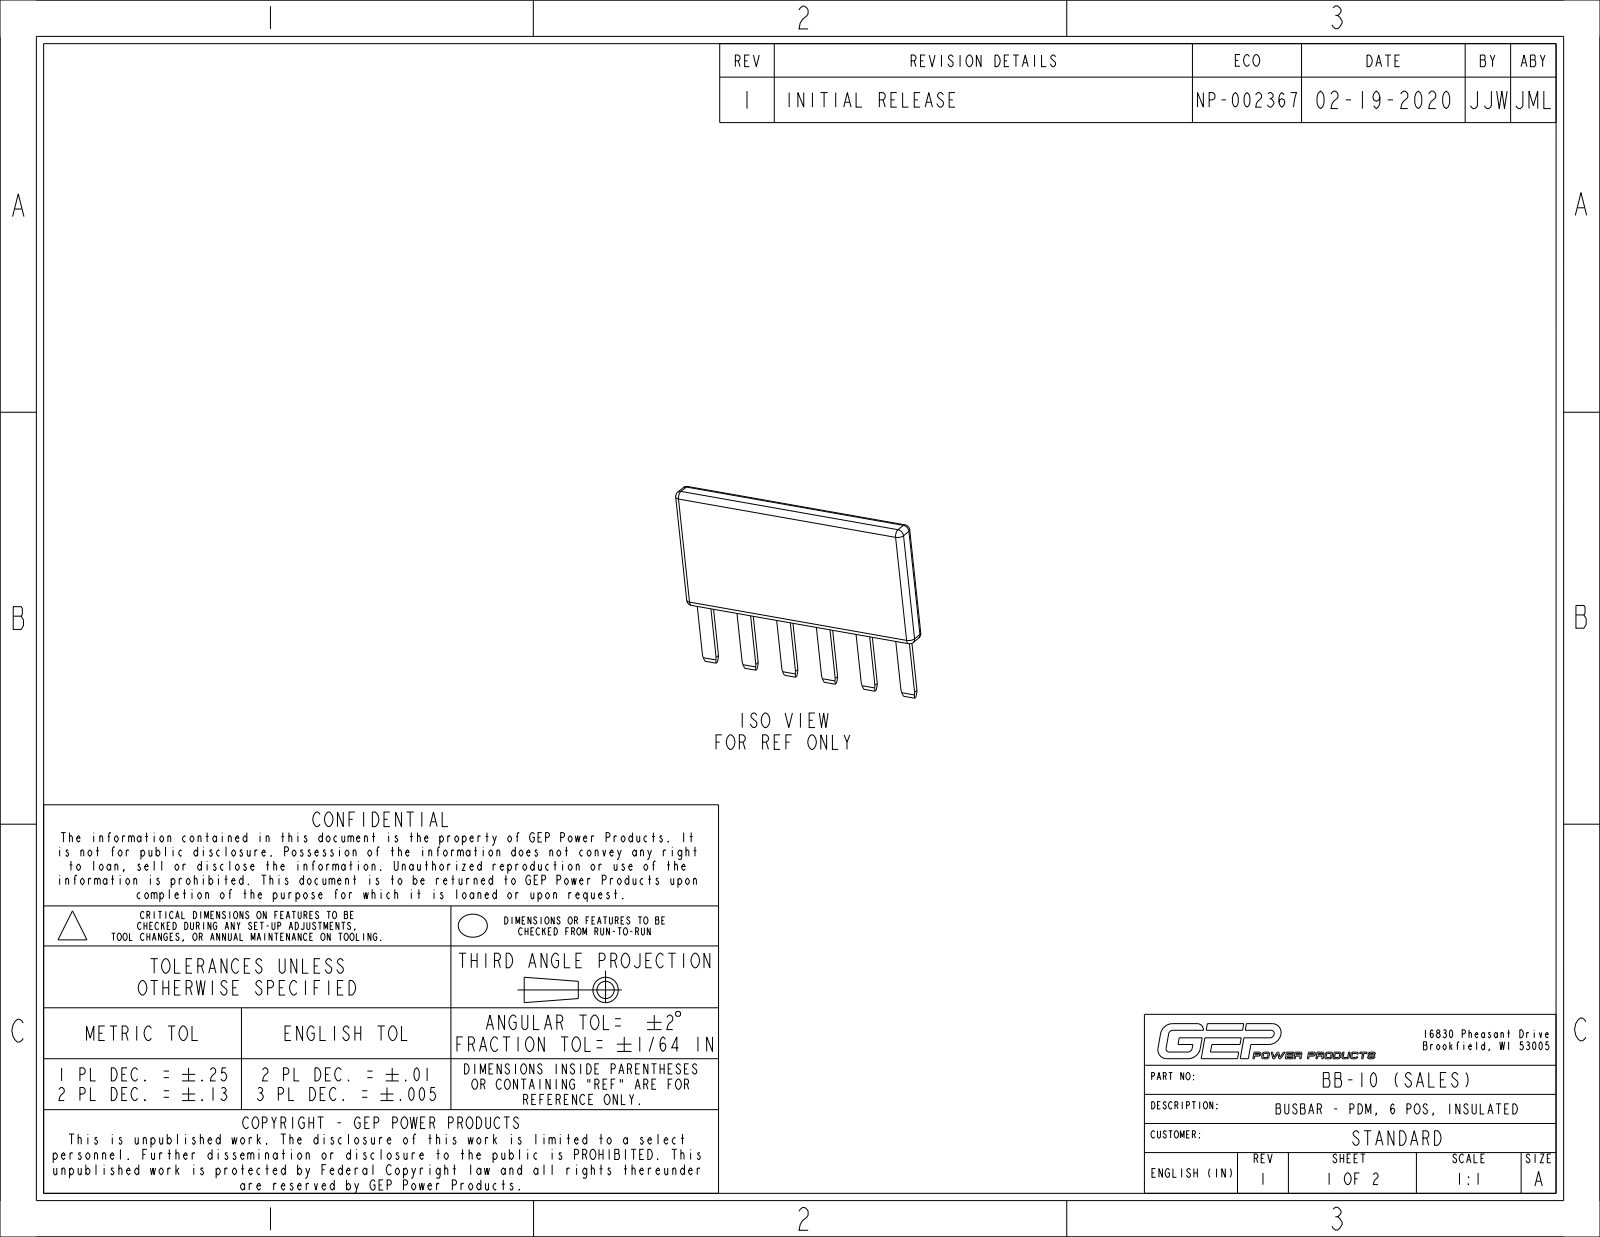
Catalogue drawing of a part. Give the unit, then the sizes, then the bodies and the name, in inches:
Units: inches
Overall size (bounding box): 1.83 × 1.31 × 0.152
Partial cylindrical surfaces — rounded edges, fillets, slot ends (radius × count): R0.04 ×12
Main face-to-face distances: 0.032, 0.06, 0.06, 0.092, 0.152, 0.092, 0.81, 0.75, 0.32, 0.87
Volume: 0.247 in³ · Surface area: 10.14 in²
Bodies: 2 solids, 96 faces (76 planar, 12 cylindrical, 8 other)
Part name (STEP PRODUCT): Q-BB-10_BAR_NCF; Q-BB-10_MOLD_NCF; Q-BB-10_NCF_ASM; Q-BB-10_SALES_NCF_ASM
STEP written by: CREO PARAMETRIC BY PTC INC, 2017110 (CONFIG_CONTROL_DESIGN)
